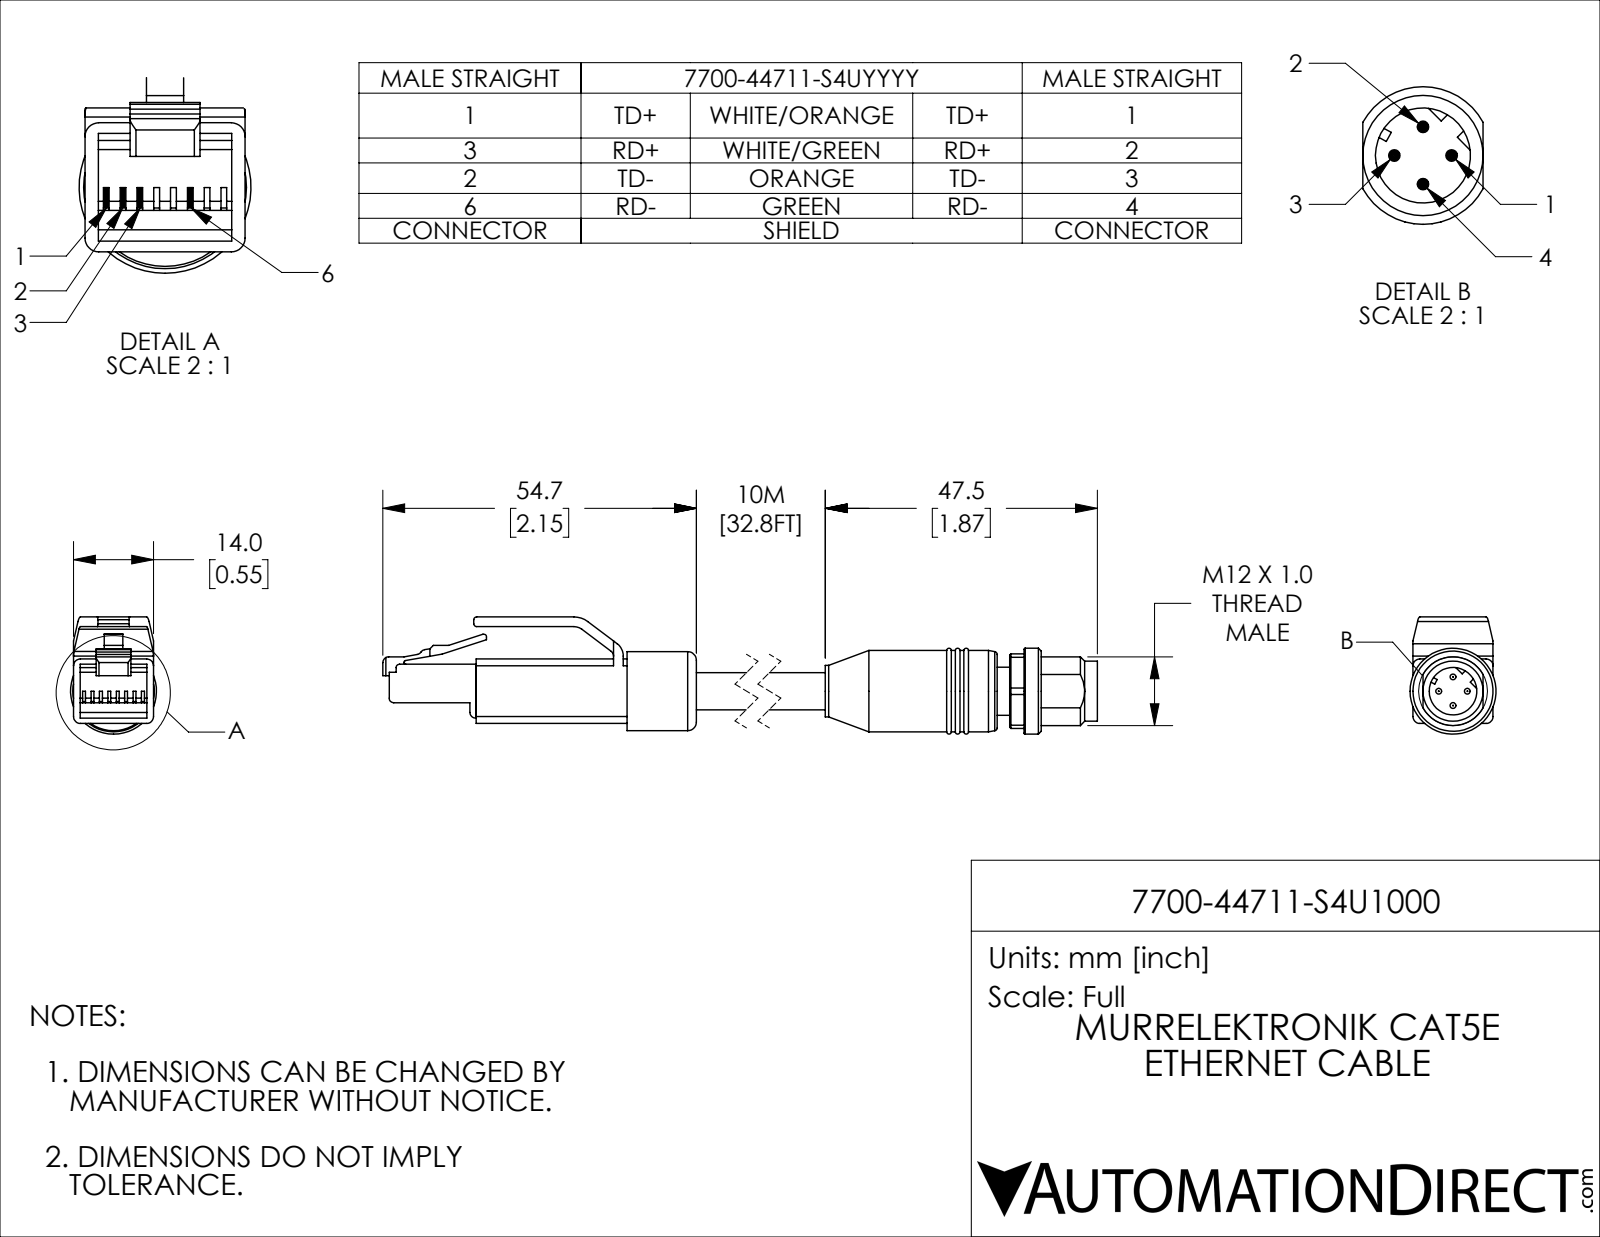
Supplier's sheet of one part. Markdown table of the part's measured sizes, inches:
| quantity | value |
| --- | --- |
| part name | 7700-44711-S4U1000_2; 7700-44711-S4U1000_1; 7700-44711-S4U1000 |
| STEP written by | SolidWorks 2021 (CONFIG_CONTROL_DESIGN) |
| units | inches |
| bodies | 3 solids, 266 faces (151 planar, 73 cylindrical, 42 other) |
| overall size | 5.854 × 0.806 × 0.591 |
| volume | 0.912 in³ |
| surface area | 11.41 in² |
| round holes (diameter × count) | 0.327 × 1 |
| round bosses / shafts (diameter × count) | 0.039 × 4, 0.591 × 1, 0.559 × 1, 0.543 × 1, 0.413 × 1, 0.354 × 1, 0.331 × 1, 0.256 × 1 |
| partial cylindrical surfaces (radius × count) | 0.047 × 6, 0.02 × 5, 0.039 × 5, 0.012 × 2, 0.024 × 1, 0.031 × 1, 0.091 × 1, 0.106 × 1 |
| main face-to-face distances | 0.444, 0.55, 0.067, 0.046, 0.504, 0.037, 0.407, 0.222, 0.665, 0.732 |
